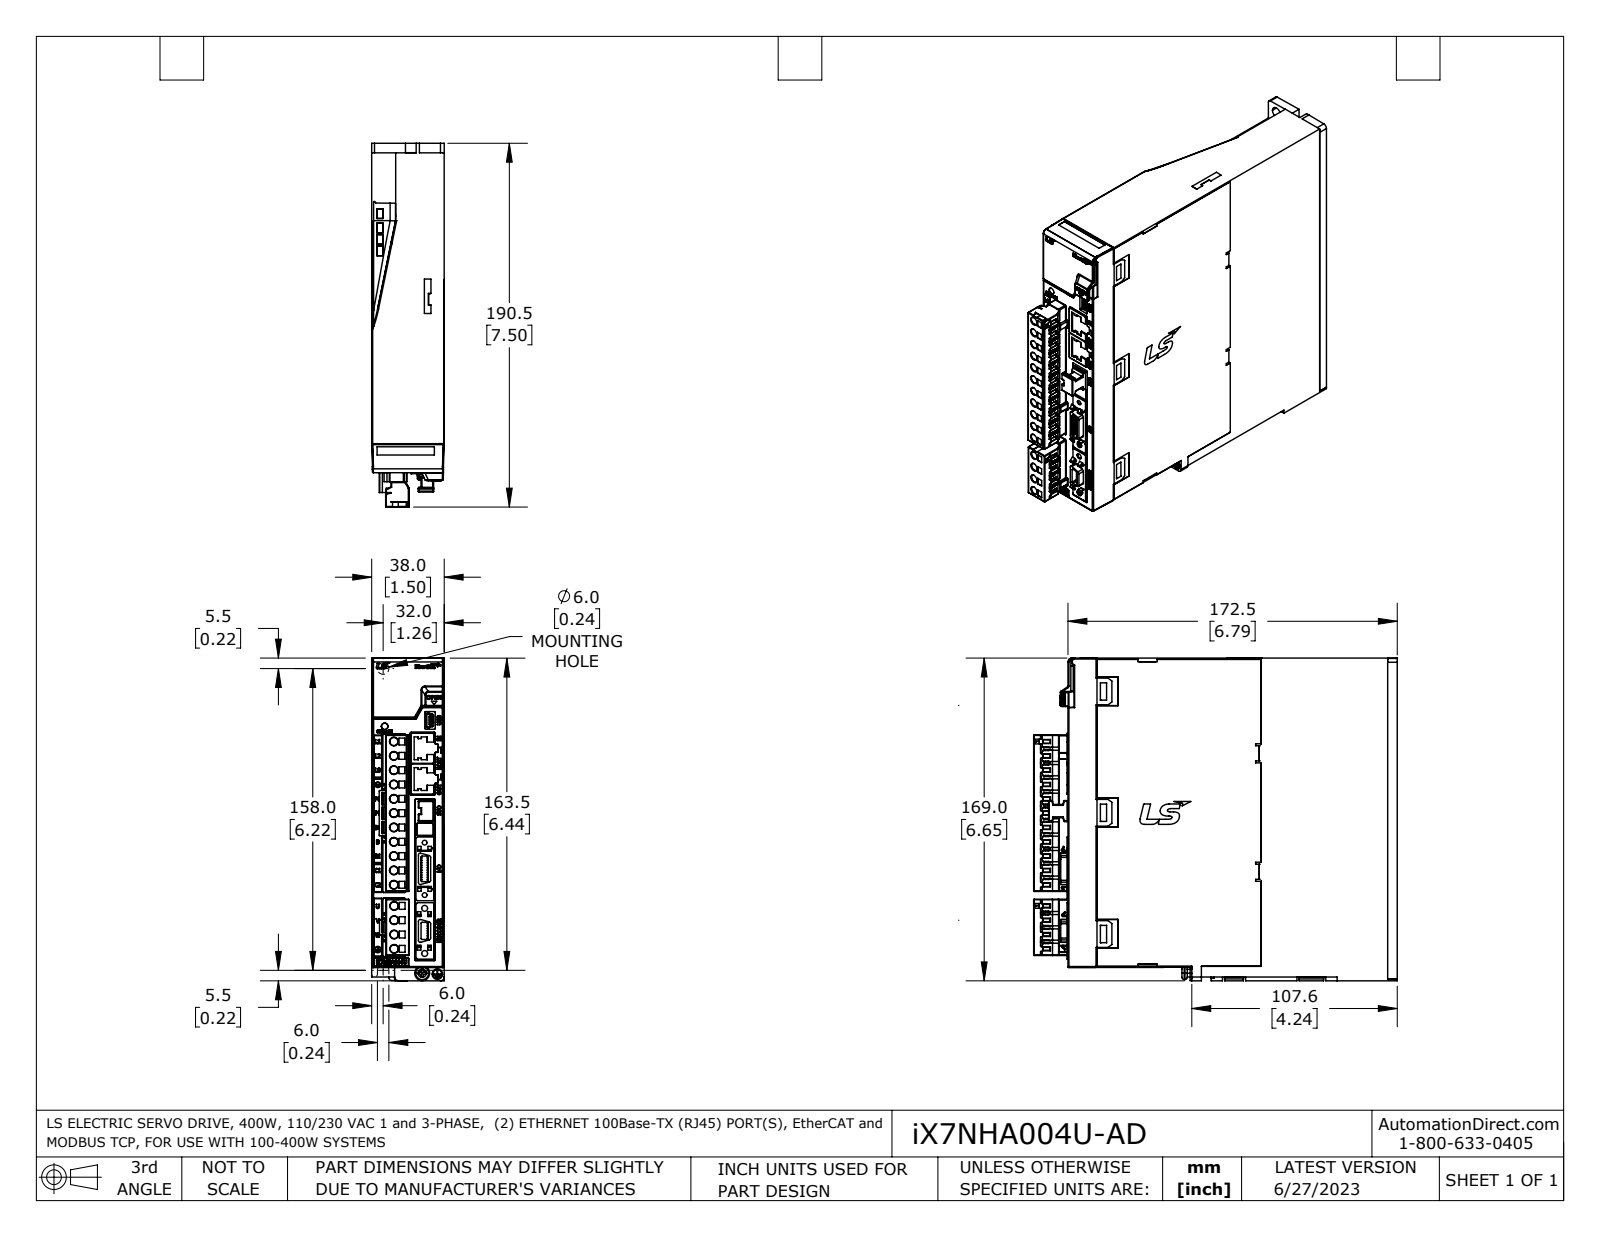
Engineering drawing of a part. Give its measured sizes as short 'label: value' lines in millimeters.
name: OUTLINE (iX7NHA004U) 30 faces broken 1 BODY Only 1B w 2cc srd1bDb 2 w NEWFACE BaCLIPS cmbB n TBs 2c fxt sr1
written by: SolidWorks 2021 (AUTOMOTIVE_DESIGN)
unit: mm
bodies: 6 solids, 4679 faces (3356 planar, 550 cylindrical, 773 other)
size: 190.5 × 169.1 × 38
volume: 1 073 000 mm³; area: 120 000 mm²
holes: 15× ⌀4.2, 2× ⌀2.5, 2× ⌀3.1, 1× ⌀2, 1× ⌀2.4, 1× ⌀2.9, 1× ⌀3.3, 1× ⌀5.5, 1× ⌀6
bosses: 1× ⌀7.8, 1× ⌀6.7, 1× ⌀4.7, 1× ⌀4, 1× ⌀3.4, 1× ⌀3
rounds: 146× R0.3, 115× R0.5, 69× R0.4, 31× R0.2, 10× R0.7, 8× R0.9, 5× R1, 5× R2
face distances: 38, 38, 0.5, 157.3, 157.8, 15.2, 172.5, 14.7, 167, 172.4
hole spacings: 7.5, 15, 22.5, 30, 37.5, 45, 33.6, 41
